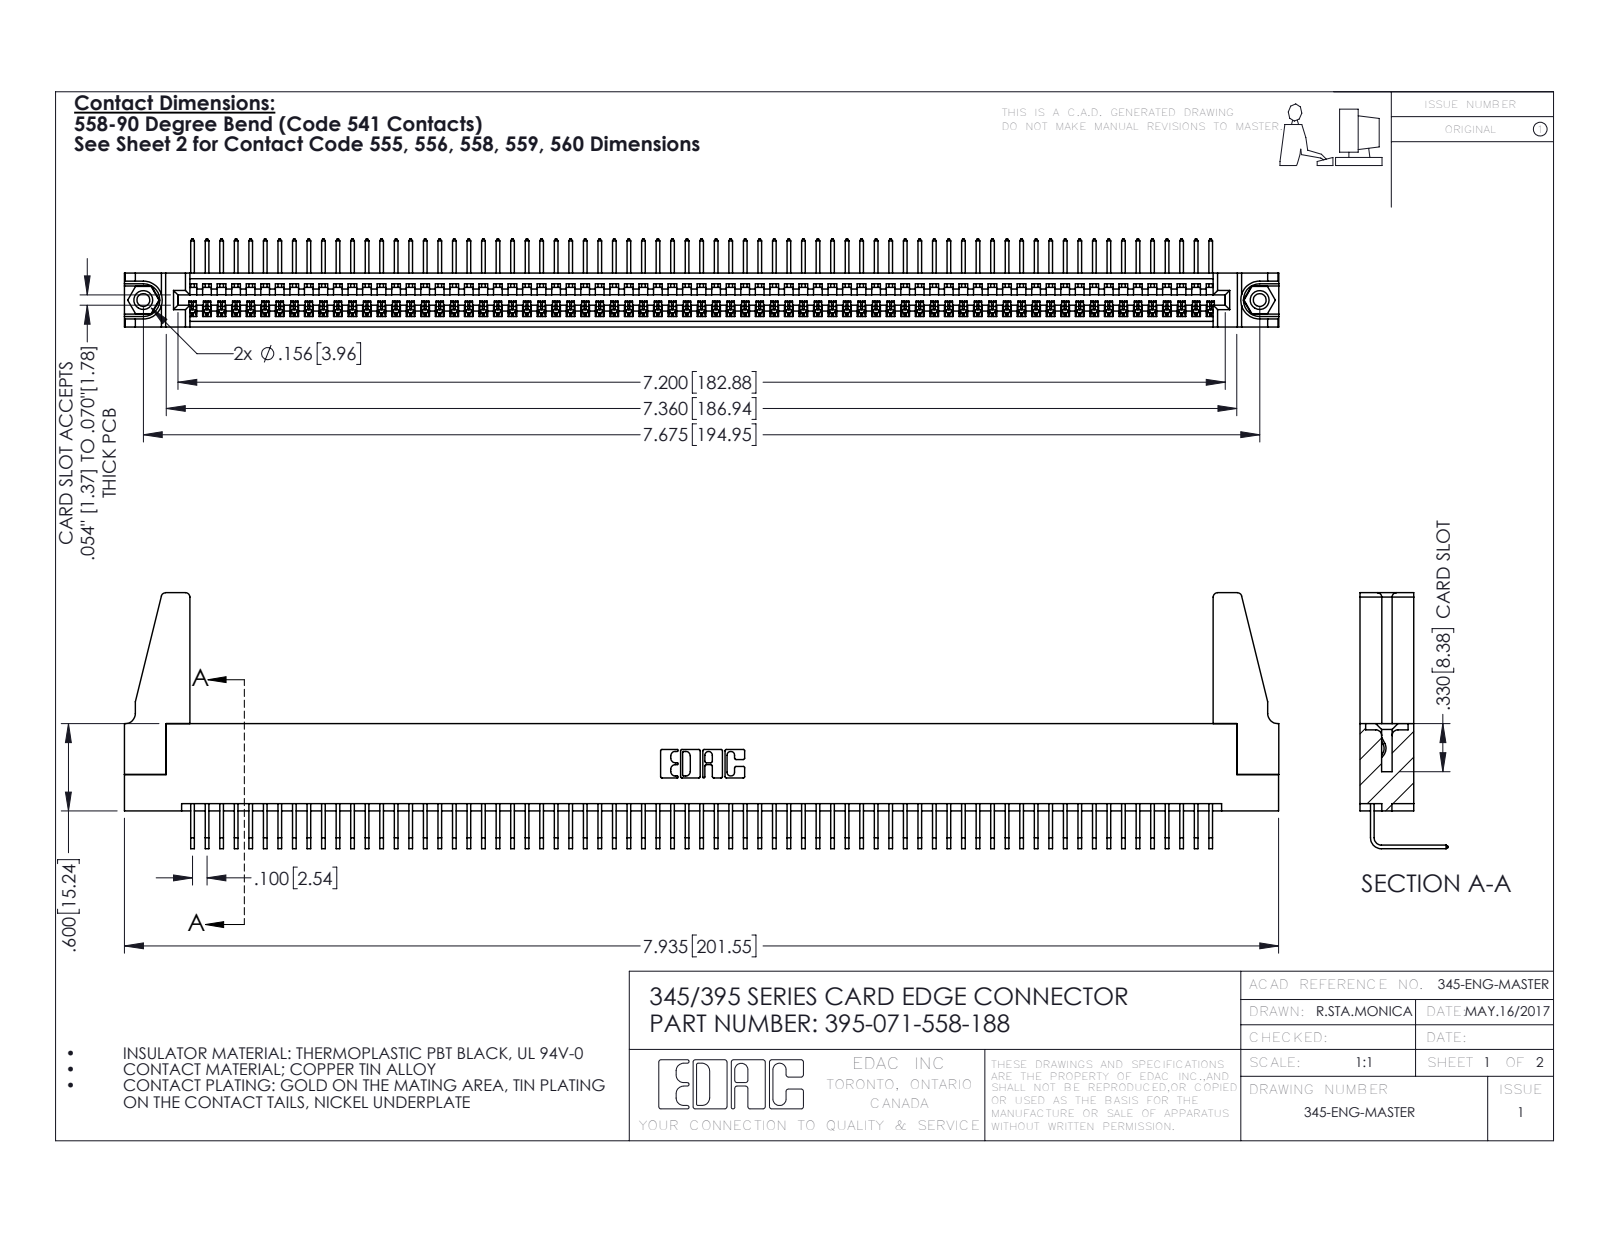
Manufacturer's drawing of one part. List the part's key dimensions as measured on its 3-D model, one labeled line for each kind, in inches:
Part name (STEP PRODUCT): 345-220-078_345-220-088; 345-292-001_558 Tail - 2; 345-250-001_345-250-001-102; 345 Part_Flush Mounting Lugs - 0.156 Dia-TH (+1 more)
STEP written by: SolidWorks 2016 (CONFIG_CONTROL_DESIGN)
Units: inches
Bodies: 76 solids, 4510 faces (3134 planar, 1360 cylindrical, 16 other)
Overall size (bounding box): 7.936 × 1.759 × 0.605
Volume: 1.396 in³ · Surface area: 48.03 in²
Round holes (diameter × count): ⌀0.089 ×2, ⌀0.125 ×2, ⌀0.156 ×2, ⌀0.064 ×1
Round bosses / shafts (diameter × count): ⌀0.155 ×2
Partial cylindrical surfaces — rounded edges, fillets, slot ends (radius × count): R0.006 ×142, R0.01 ×22, R0.03 ×8, R0.007 ×6, R0.031 ×6, R0.026 ×3, R0.031 ×2, R0.04 ×2
Main face-to-face distances: 0.072, 0.298, 0.37, 0.2, 0.098, 0.272, 0.025, 0.225, 0.149, 0.072
Hole centre spacings: 0.27, 7.439, 7.675
